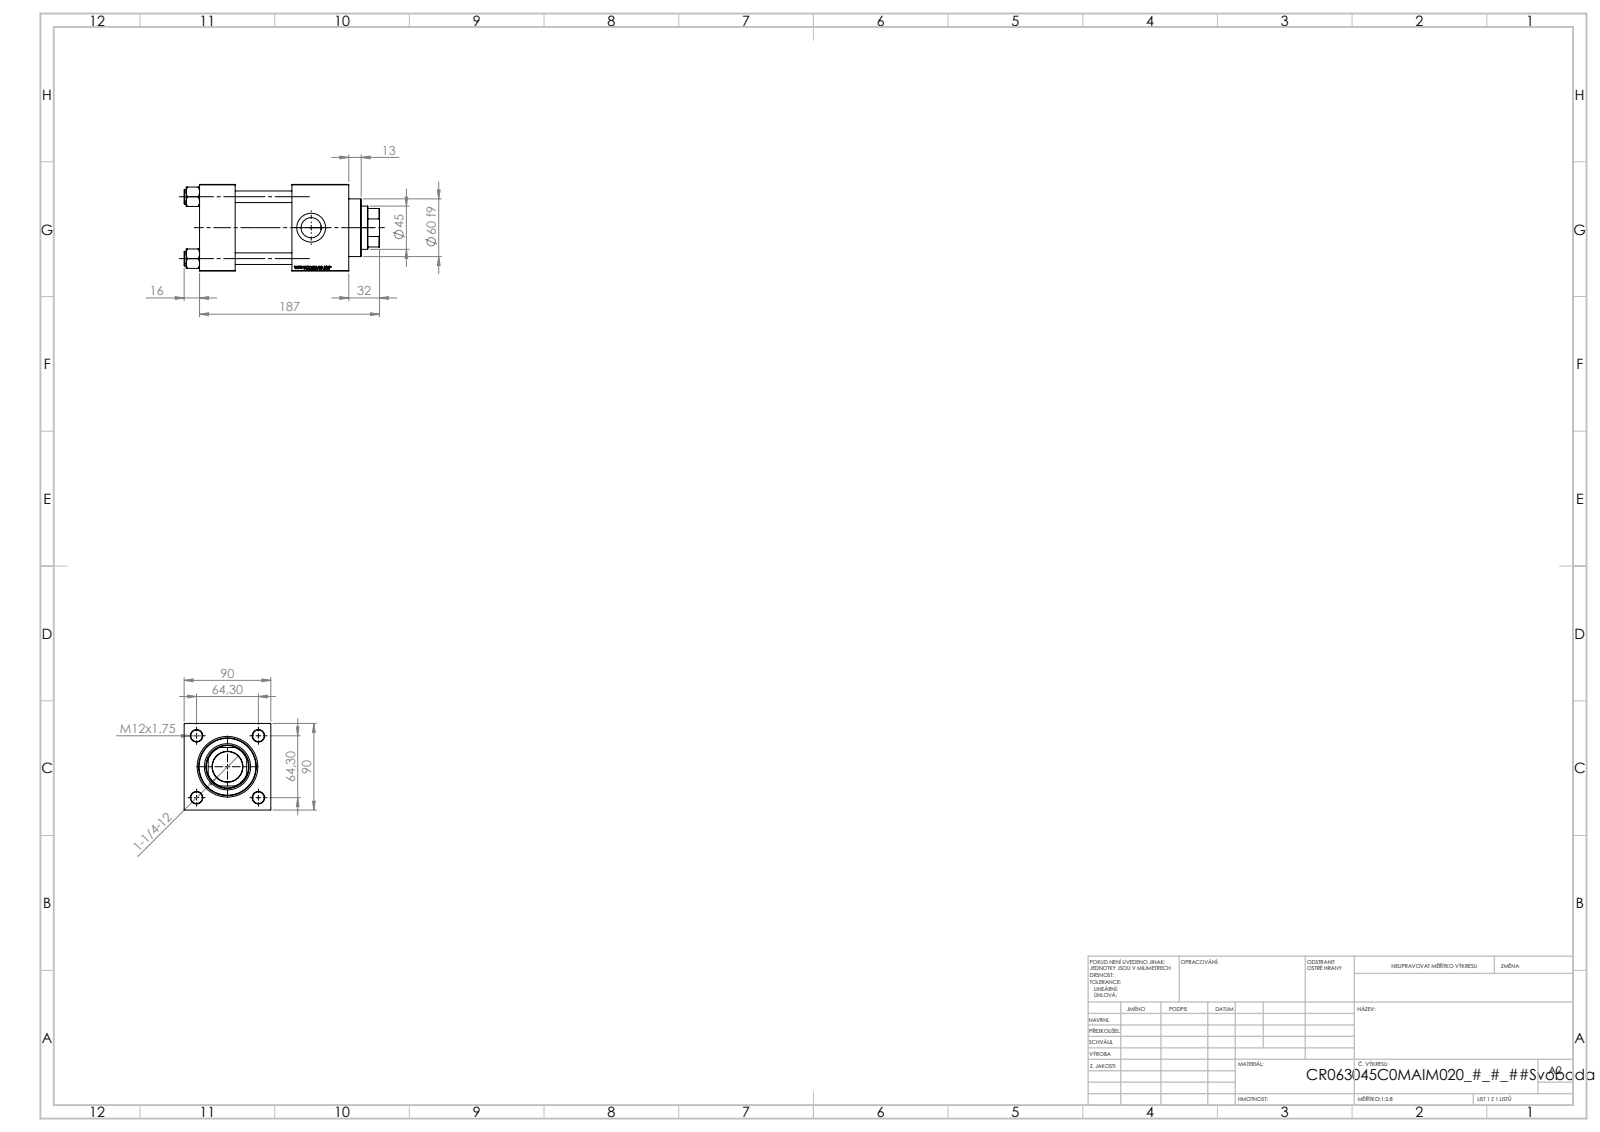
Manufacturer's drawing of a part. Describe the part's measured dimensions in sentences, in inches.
The part is named "NUT_M5_C; V215CR_VCP_C; V215CR_C_Body; V215_VC_A (+1 more)". Its 3-D file was written by "SolidWorks 2019 (CONFIG_CONTROL_DESIGN)". It is 11 solids with 1146 faces: 525 planar, 85 cylindrical and 536 other. Overall it measures 7.992 by 3.543 by 3.543 inches. Its volume is 60.89 cubic inches and its surface area 294.4 square inches. Round holes: 4 of diameter 0.472, 2 of diameter 0.276, 2 of diameter 0.825, 2 of diameter 1.181, 1 of diameter 1.24, 1 of diameter 1.772, 1 of diameter 1.89, 1 of diameter 1.969, 1 of diameter 2.362, 1 of diameter 2.48. Round bosses or shafts: 4 of diameter 0.591, 1 of diameter 2.717. Partial cylindrical surfaces (rounded edges, fillets, slot ends): 1 of radius 0.866. The main face-to-face distances are 3.543, 2.323, 1.457, 3.78, 6.102, 4.646, 4.972, 3.516, 1.193, 1.13. The hole center spacings are 1.79, 2.531, 3.58.
